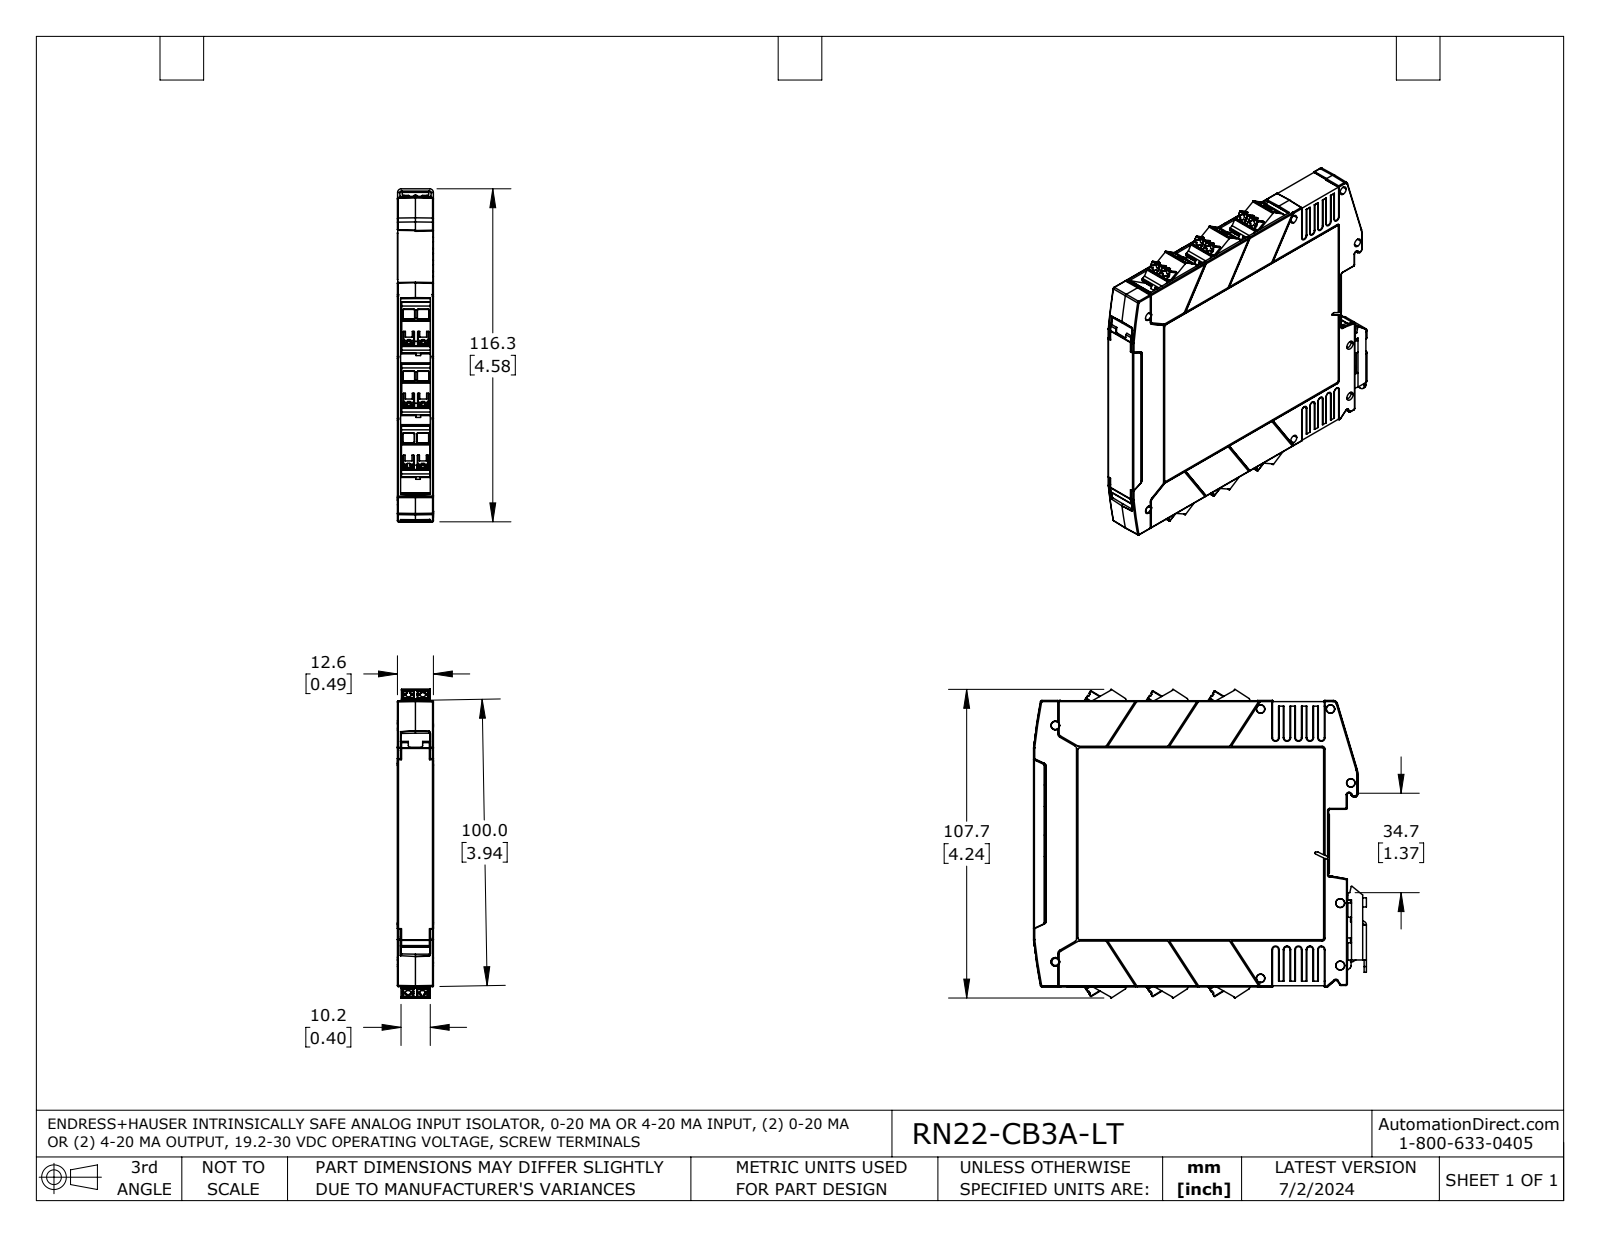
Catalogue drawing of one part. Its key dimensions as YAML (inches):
part_name: "RN22-CB3A-LT"
step_written_by: "SolidWorks 2021 (AUTOMOTIVE_DESIGN)"
units: inches
bodies: {solids: 2, faces: 3045, planar: 1939, cylindrical: 765, other: 341}
overall_size: [4.577, 4.242, 0.496]
volume: 8.127
surface_area: 58.24
round_holes:
  - {diameter: 0.118, count: 3}
  - {diameter: 0.009, count: 2}
  - {diameter: 0.097, count: 1}
  - {diameter: 0.111, count: 1}
partial_cylinders:
  - {radius: 0.008, count: 149}
  - {radius: 0.02, count: 71}
  - {radius: 0.012, count: 66}
  - {radius: 0.039, count: 28}
  - {radius: 0.005, count: 16}
  - {radius: 0.114, count: 12}
  - {radius: 0.009, count: 10}
  - {radius: 0.024, count: 10}
face_to_face_distances: [0.494, 0.043, 0.451, 0.039, 0.447, 0.047, 0.491, 0.435, 0.392, 0.031]
hole_center_spacings: [2.832, 4.477, 0.759, 0.76, 0.961, 2.073, 2.074, 3.031]
